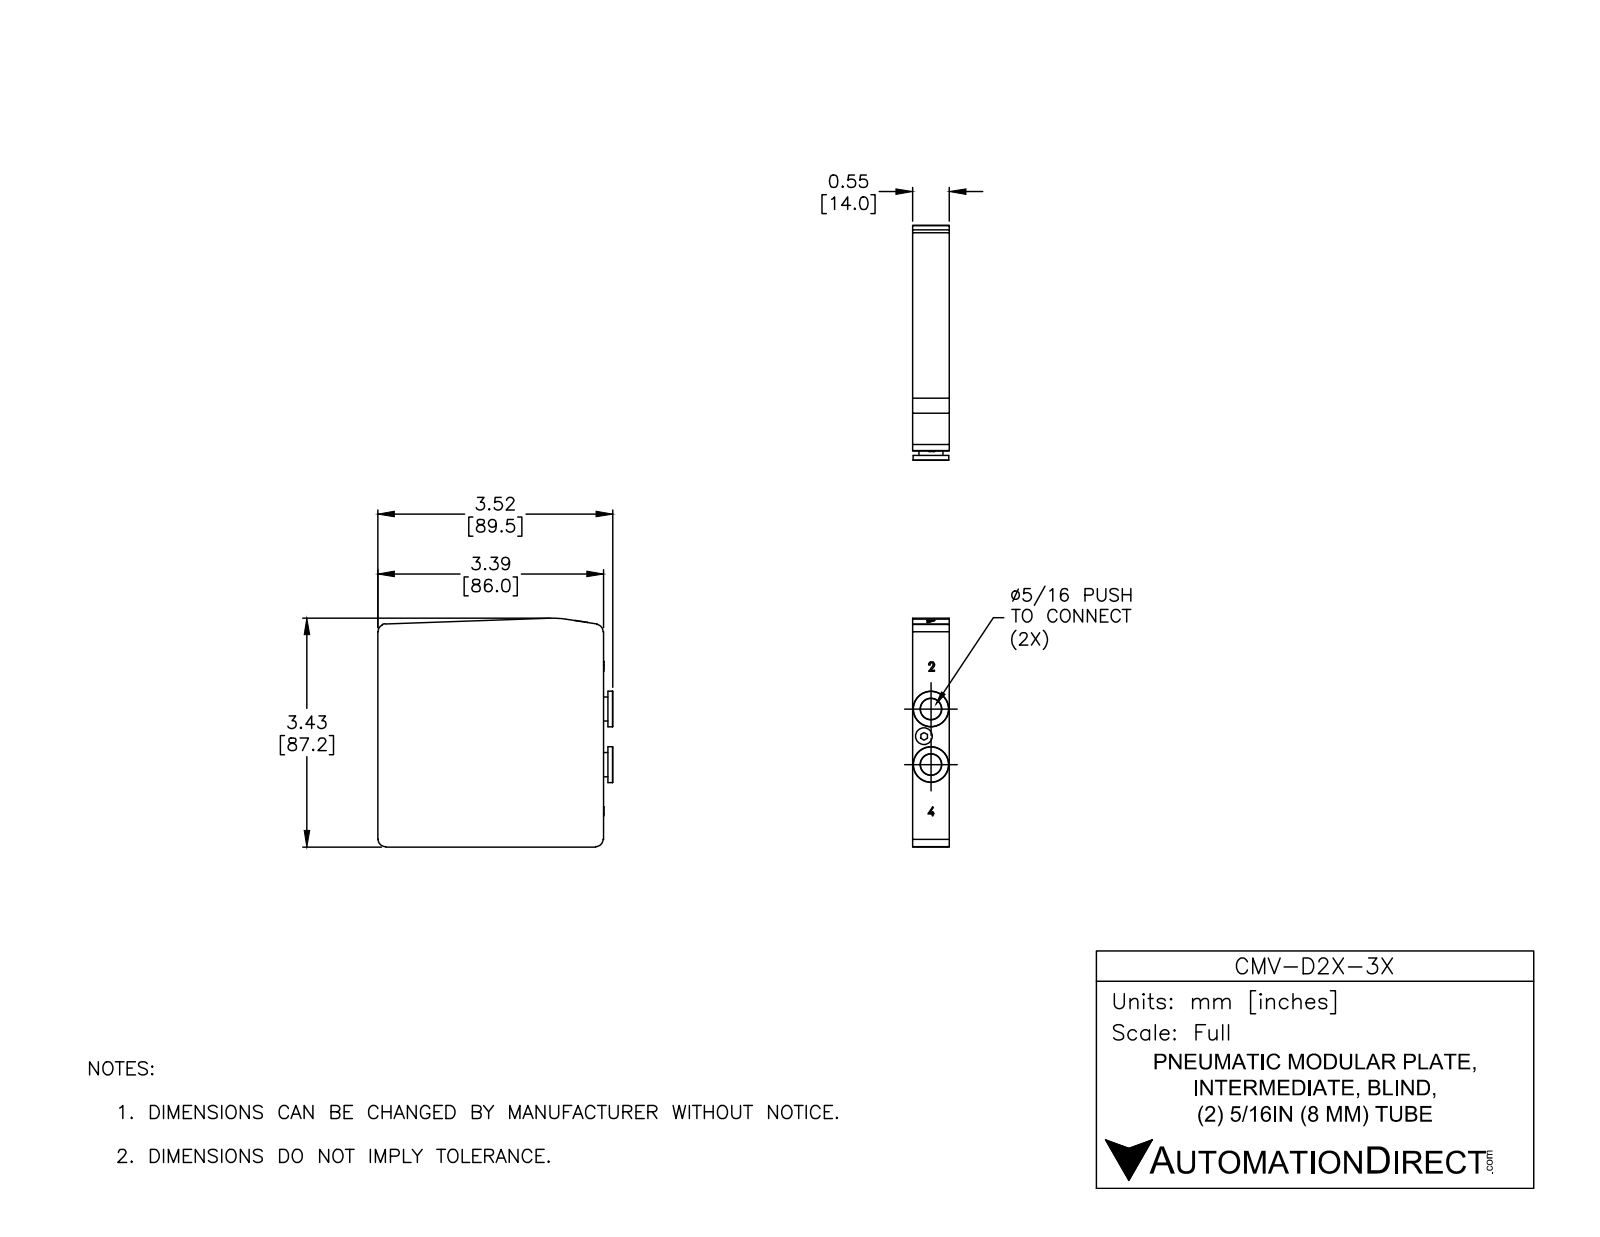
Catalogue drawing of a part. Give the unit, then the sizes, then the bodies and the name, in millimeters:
Units: millimetres
Overall size (bounding box): 89.5 × 87.22 × 14
Round holes (diameter × count): ⌀8 ×2, ⌀6.4 ×1
Round bosses / shafts (diameter × count): ⌀13.6 ×2, ⌀9.2 ×2
Partial cylindrical surfaces — rounded edges, fillets, slot ends (radius × count): R2.8 ×4, R0.17 ×1, R0.55 ×1, R0.61 ×1, R0.92 ×1, R0.96 ×1, R0.98 ×1, R0.99 ×1
Main face-to-face distances: 14, 86, 89.5, 3.5, 1.6, 87.6, 1.9, 85.8, 2.5, 1.8
Hole centre spacings: 10.72, 11.11, 21.2
Volume: 103 847 mm³ · Surface area: 20 305 mm²
Bodies: 1 solid, 107 faces (63 planar, 36 cylindrical, 8 other)
Part name (STEP PRODUCT): CMV-D2X-3X
STEP written by: SolidWorks 2017 (AUTOMOTIVE_DESIGN)
